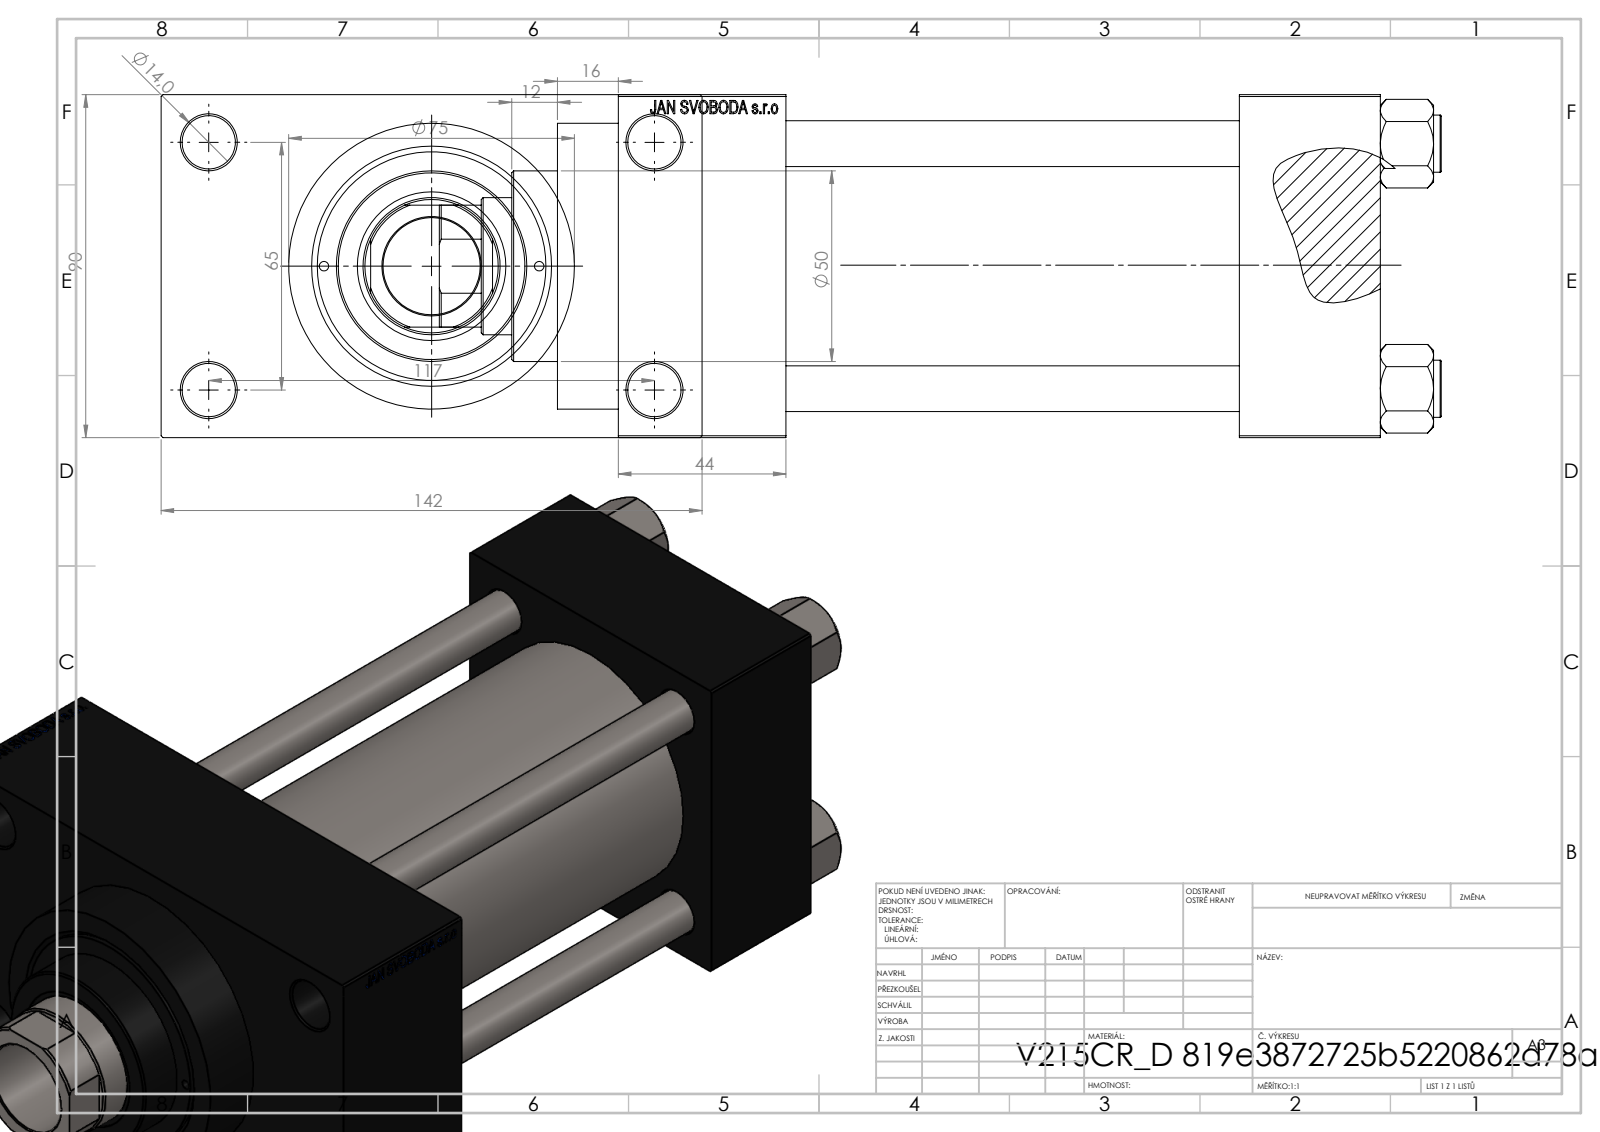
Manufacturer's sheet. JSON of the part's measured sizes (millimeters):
{"part_name": "V215CR_D_TYCINKA; V215CR_D_Body; V215CR_VCP_D; V215_VC_A (+1 more)", "step_written_by": "SolidWorks 2019 (CONFIG_CONTROL_DESIGN)", "units": "millimeters", "bodies": {"solids": 11, "faces": 1111, "planar": 499, "cylindrical": 92, "other": 520}, "overall_size": [263, 142, 90], "volume_mm3": 1237000, "surface_area_mm2": 246415, "round_holes": [[12, 4], [14, 4], [2.5, 2], [7, 2], [20.96, 2], [30, 2], [25.5, 1], [36, 1], [39, 1], [50, 1], [60, 1], [63, 1]], "round_bosses_or_shafts": [[15, 4], [75, 1], [69, 1]], "partial_cylinders_radius": [[17.5, 1]], "face_to_face_distances": [90, 119, 37, 156, 200, 163, 44, 26, 116, 142], "hole_center_spacings": [26.35, 32.39, 44.4, 45.47, 64.3, 66.92, 68.42, 69.81]}
